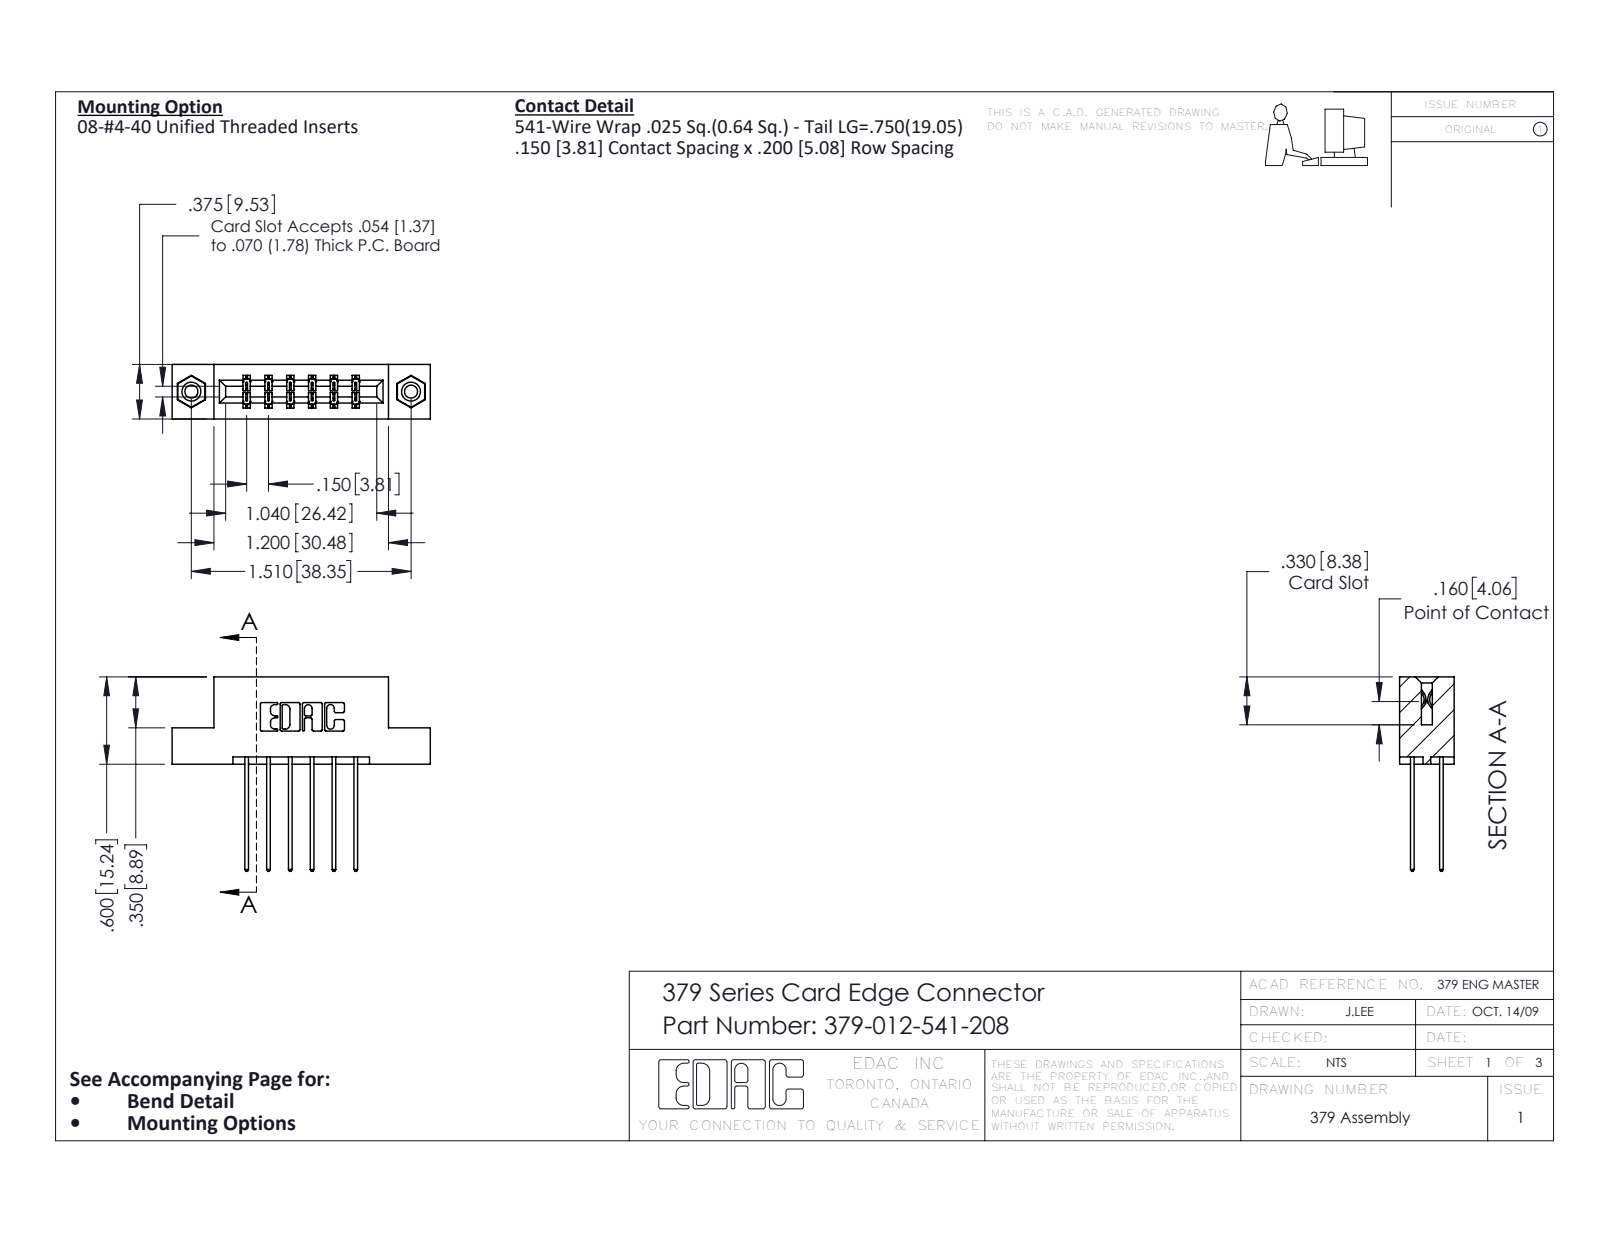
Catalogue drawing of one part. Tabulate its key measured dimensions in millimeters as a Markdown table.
| quantity | value |
| --- | --- |
| part name | 379 Part_Flush - .156 Dia - TI; 345-250-001_345-250-003-102; 345-292-001_345-293-141; 379-012-541-208 |
| STEP written by | SolidWorks 2016 (CONFIG_CONTROL_DESIGN) |
| units | millimeters |
| bodies | 15 solids, 798 faces (534 planar, 248 cylindrical, 16 other) |
| overall size | 45.1 × 34 × 9.5 |
| volume | 4 410 mm³ |
| surface area | 4 992 mm² |
| round holes (diameter × count) | 2.3 × 2, 3.2 × 2, 4 × 2 |
| round bosses / shafts (diameter × count) | 3.9 × 2 |
| partial cylindrical surfaces (radius × count) | 0.3 × 22, 0.2 × 18, 0.3 × 12, 0.2 × 6, 0.8 × 6, 0.7 × 3, 0.4 × 2, 0.6 × 2 |
| main face-to-face distances | 7.6, 5.1, 3.8, 2.5, 9.5, 1.3, 1.9, 6.4, 8.9, 14 |
| hole center spacings | 38.4 |
